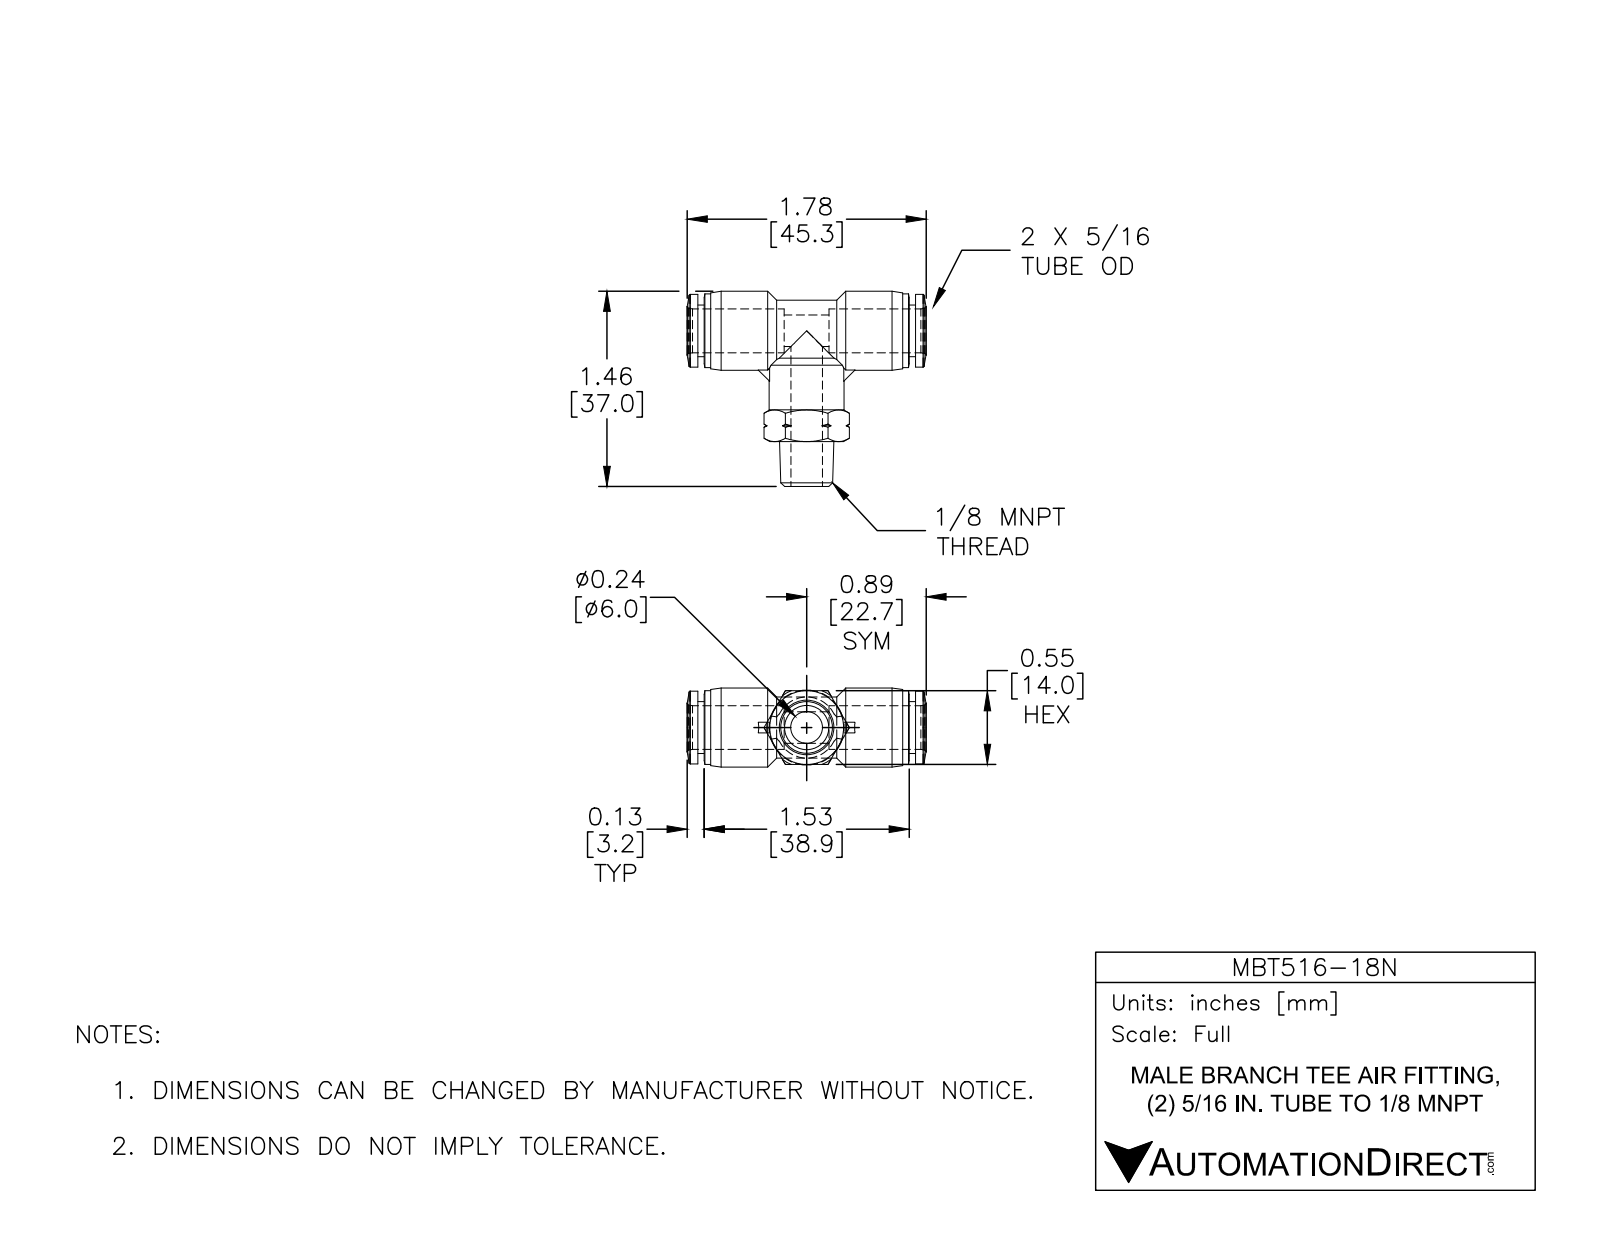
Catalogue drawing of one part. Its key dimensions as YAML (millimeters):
part_name: "MBT516-18N"
step_written_by: "SolidWorks 2015 (CONFIG_CONTROL_DESIGN)"
units: millimeters
bodies: {solids: 1, faces: 121, planar: 23, cylindrical: 34, other: 64}
overall_size: [45.3, 37, 15]
volume: 6820
surface_area: 5130
round_holes:
  - {diameter: 6, count: 2}
  - {diameter: 8.3, count: 1}
round_bosses_or_shafts:
  - {diameter: 15, count: 1}
  - {diameter: 14.2, count: 1}
  - {diameter: 14, count: 1}
  - {diameter: 13.8, count: 1}
  - {diameter: 11.6, count: 1}
  - {diameter: 9.8, count: 1}
partial_cylinders:
  - {radius: 5.8, count: 1}
face_to_face_distances: [14, 1.2, 40.1, 41.3, 8.5, 16.4, 24.9, 15.2, 23.7, 38.9]
